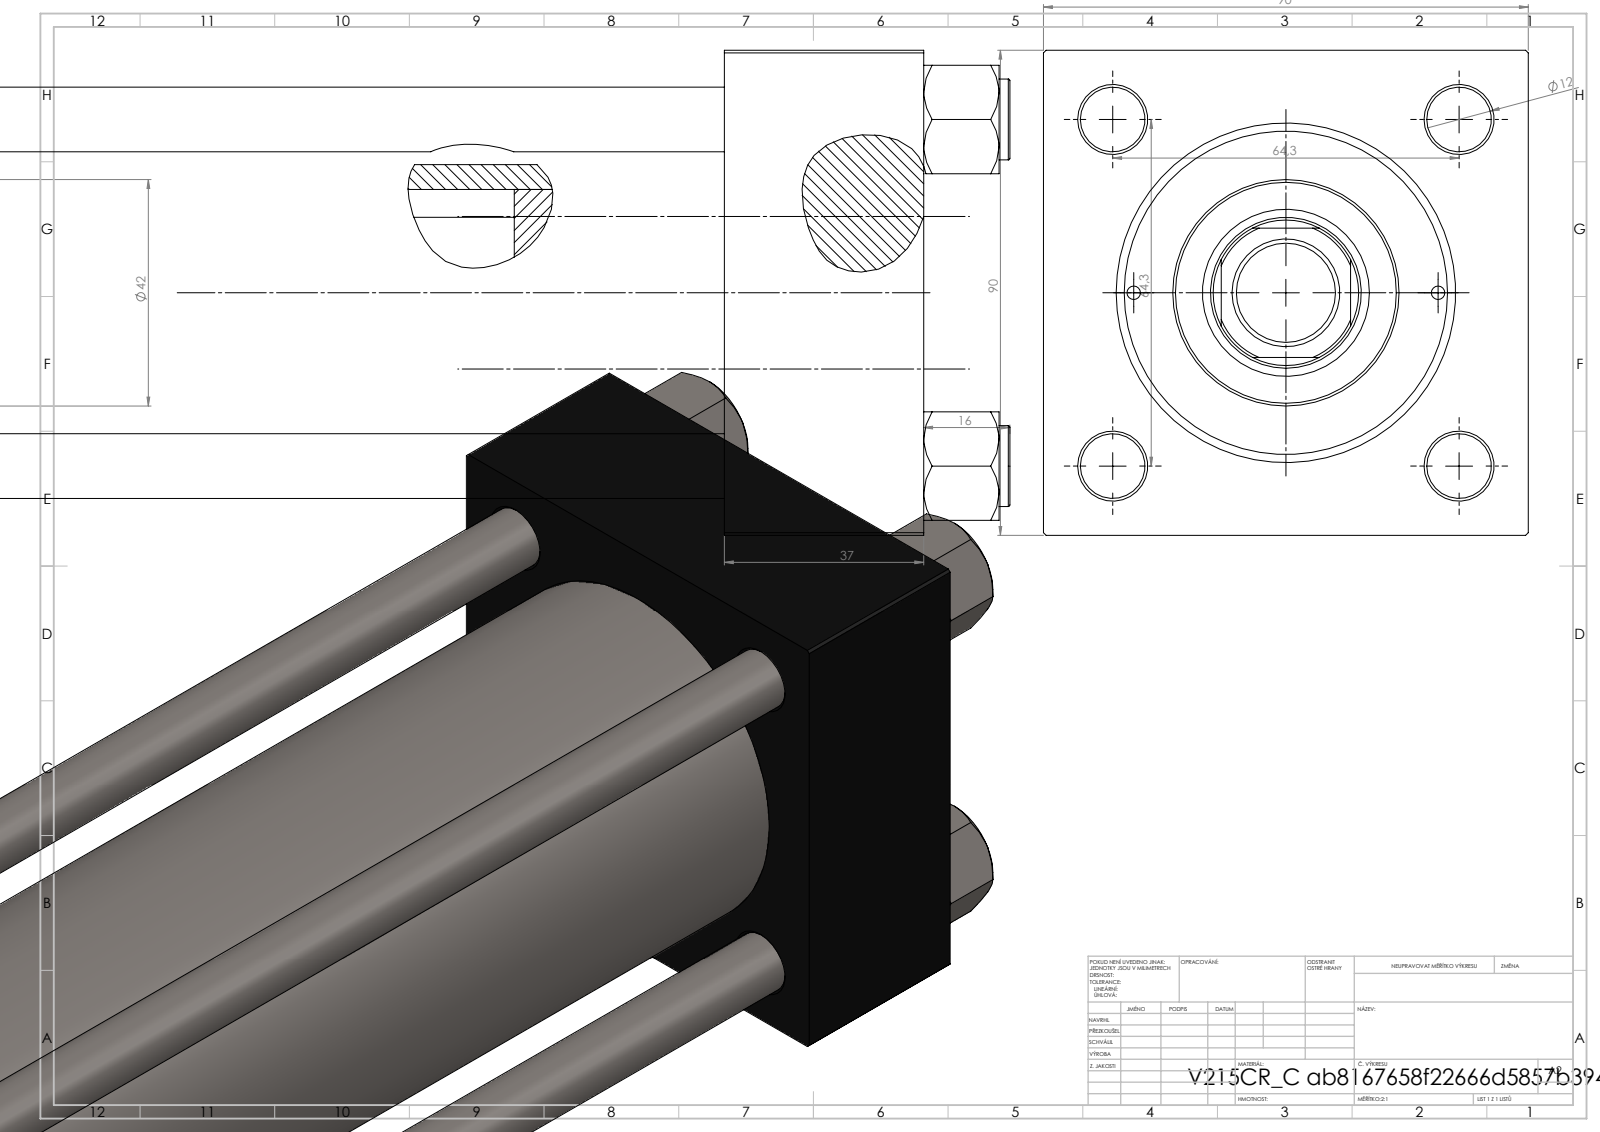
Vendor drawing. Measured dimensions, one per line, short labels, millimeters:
name: V215CR_C_TYCINKA; V215CR_VCP_C; NUT_M5_C; V215_VC_A (+2 more)
written by: SolidWorks 2019 (CONFIG_CONTROL_DESIGN)
unit: mm
bodies: 12 solids, 1168 faces (532 planar, 94 cylindrical, 542 other)
size: 611 × 90 × 90
volume: 1 598 000 mm³; area: 429 952 mm²
holes: 4× ⌀12, 2× ⌀2.5, 2× ⌀7, 2× ⌀20.96, 2× ⌀30, 1× ⌀18.5, 1× ⌀28, 1× ⌀31, 1× ⌀50, 1× ⌀60, 1× ⌀63
bosses: 4× ⌀15, 1× ⌀69, 1× ⌀42, 1× ⌀20, 1× ⌀18
rounds: 1× R13.5
face distances: 90, 37, 535, 498, 476, 439, 59, 506.3, 469.3, 30.3
hole spacings: 32.39, 45.47, 64.3, 68.42, 28.25, 90.93, 56.5, 477.5
